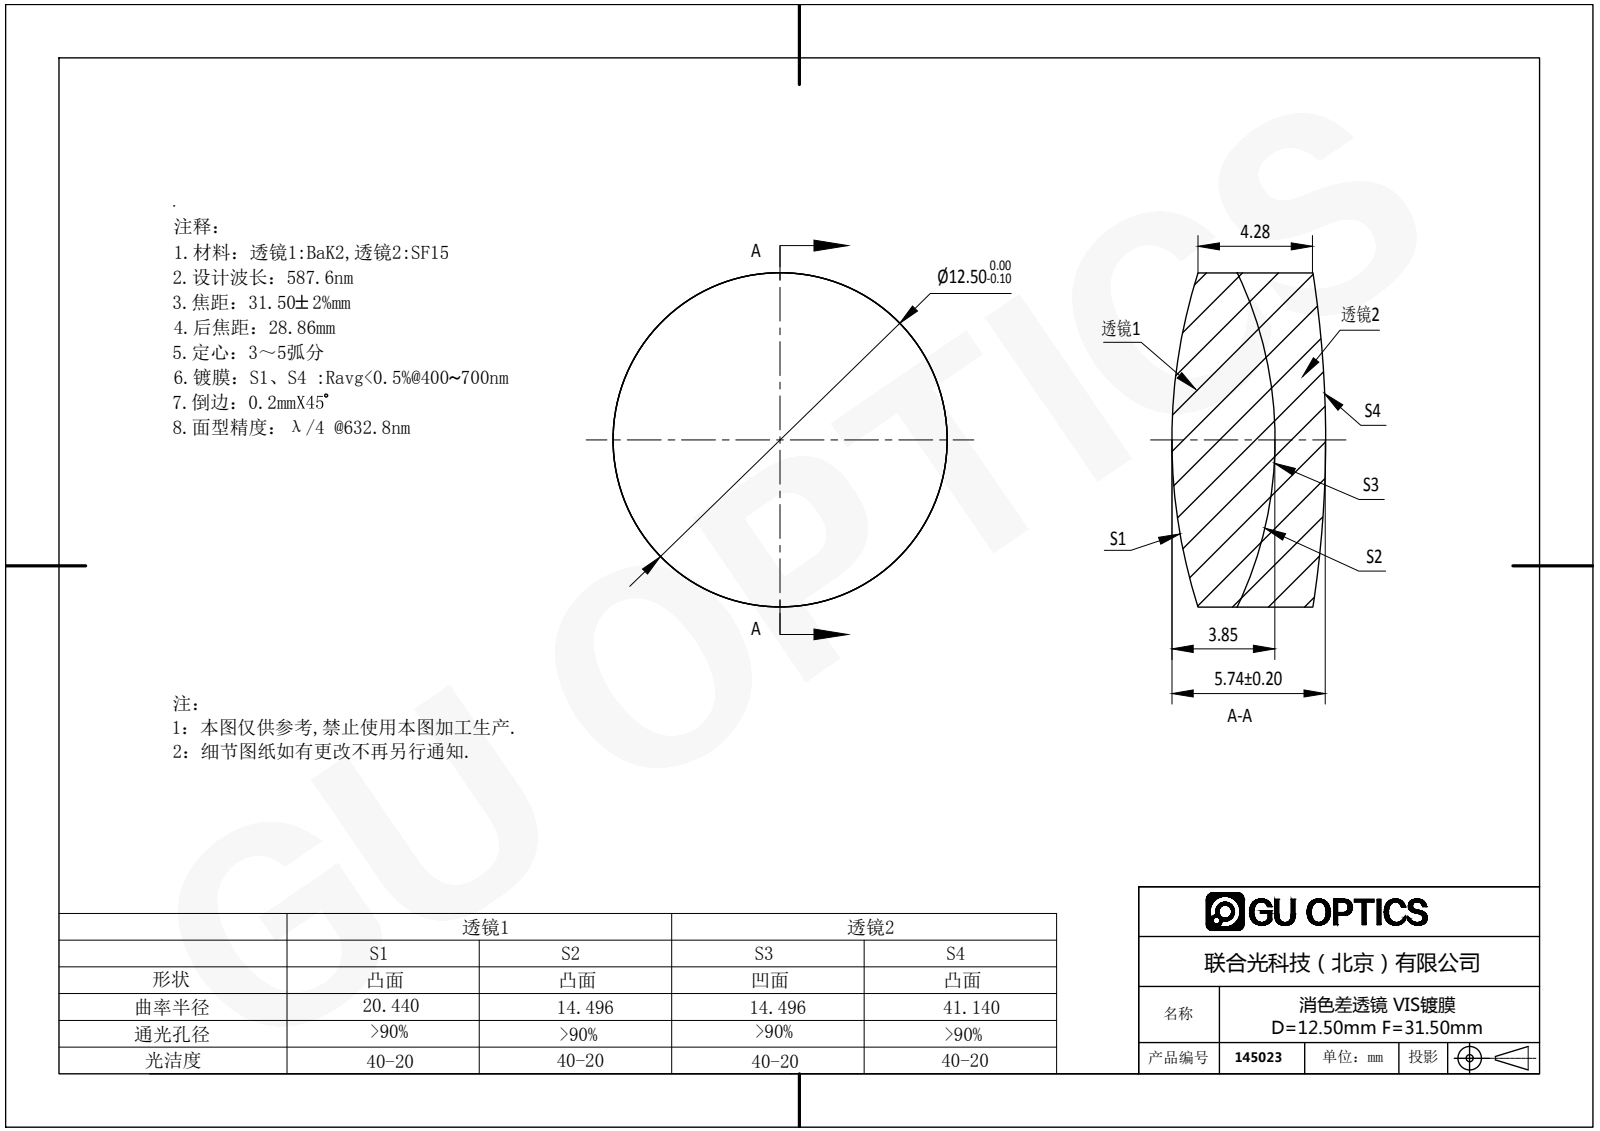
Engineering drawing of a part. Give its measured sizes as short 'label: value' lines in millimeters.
name: 145023
written by: SolidWorks 2016 (AUTOMOTIVE_DESIGN)
unit: mm
bodies: 2 solids, 12 faces (0 planar, 4 cylindrical, 8 other)
size: 12.5 × 12.5 × 5.74
volume: 616 mm³; area: 675 mm²
bosses: 1× ⌀12.5
